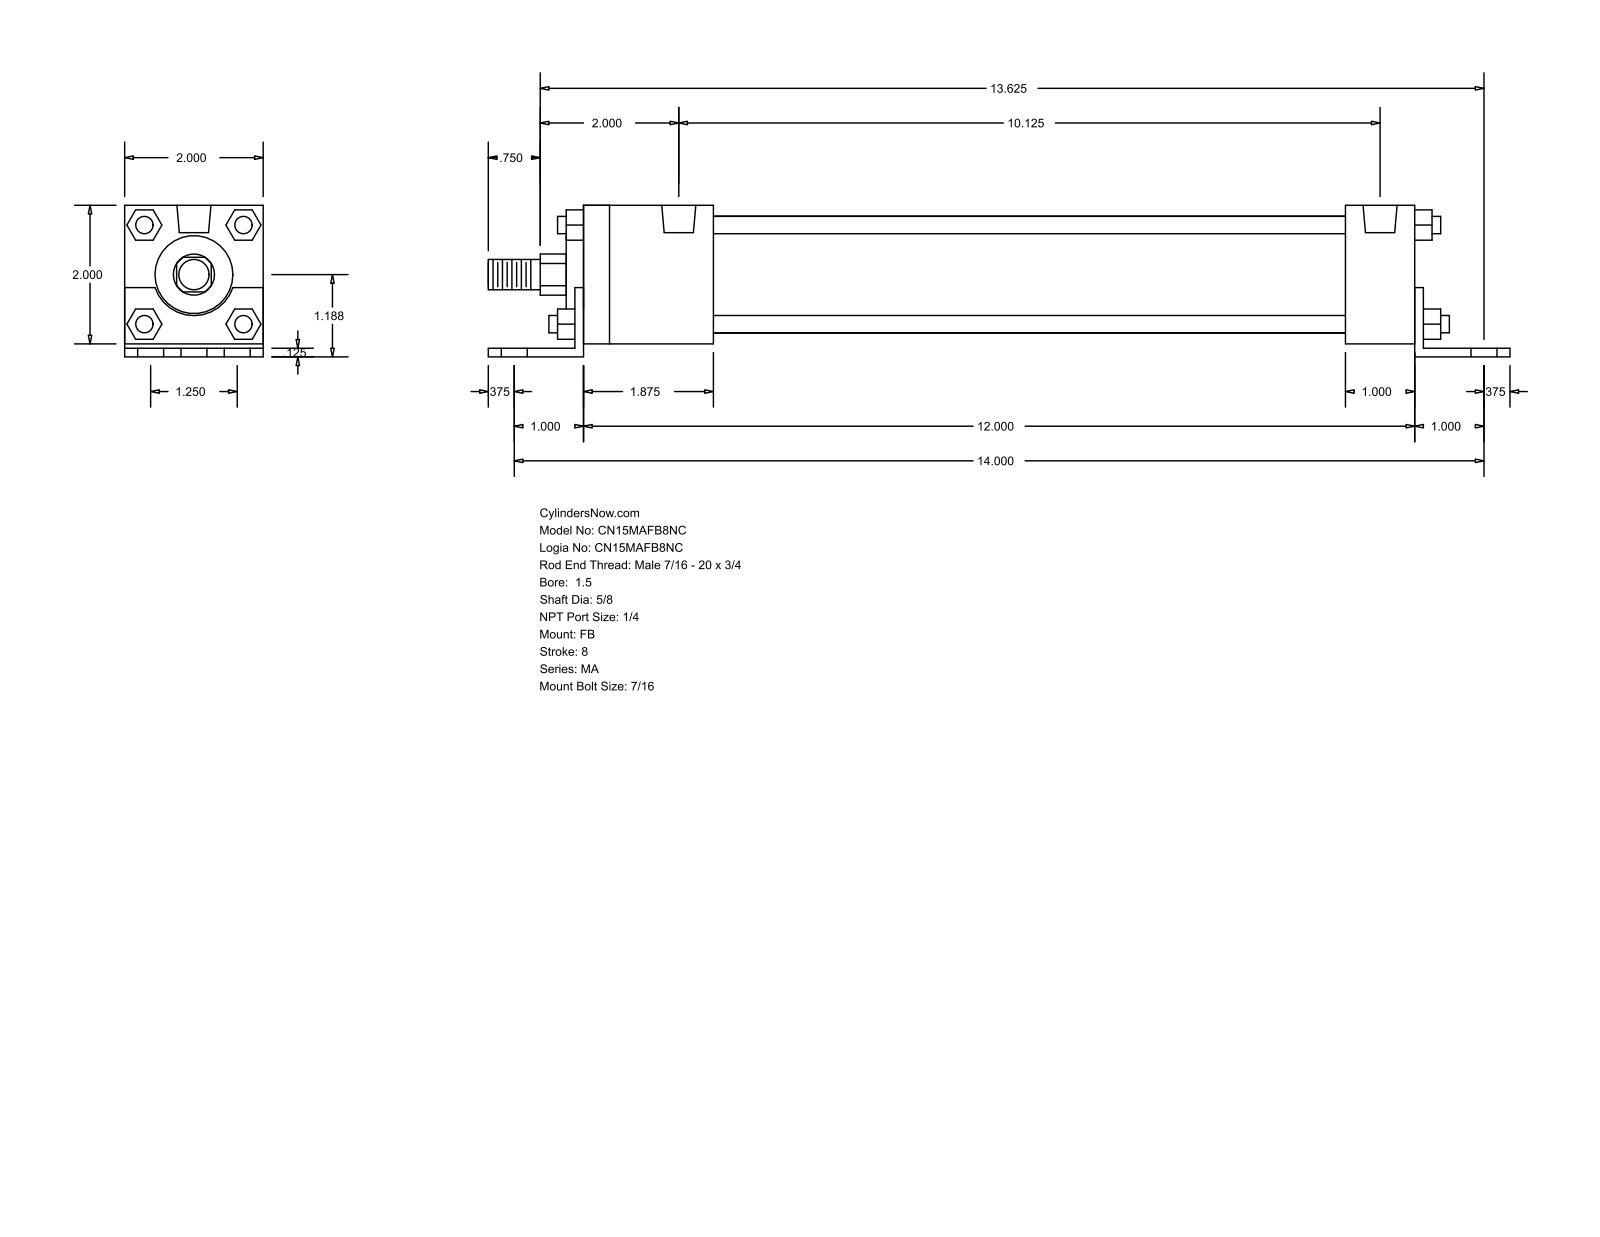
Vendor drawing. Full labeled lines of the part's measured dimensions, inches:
Part name (STEP PRODUCT): MA_FB__0150_0.625
STEP written by: GSSL Pune (CONFIG_CONTROL_DESIGN)
Units: inches
Bodies: 0 solids, 140 faces (105 planar, 35 cylindrical, 0 other)
Overall size (bounding box): 14.75 × 2.187 × 2
Round holes (diameter × count): ⌀0.437 ×6, ⌀0.313 ×4, ⌀0.492 ×2
Round bosses / shafts (diameter × count): ⌀0.25 ×4, ⌀1.69 ×1, ⌀1.125 ×1, ⌀0.625 ×1, ⌀0.437 ×1
Partial cylindrical surfaces — rounded edges, fillets, slot ends (radius × count): R0.297 ×1, R0.593 ×1
Main face-to-face distances: 2, 0.125, 0.187, 2.187, 0.063, 2.063, 1.125, 12.25, 0.125, 12.375
Hole centre spacings: 0.625, 14.014, 14, 1.25, 1.625, 2.456, 10.125, 11.642
